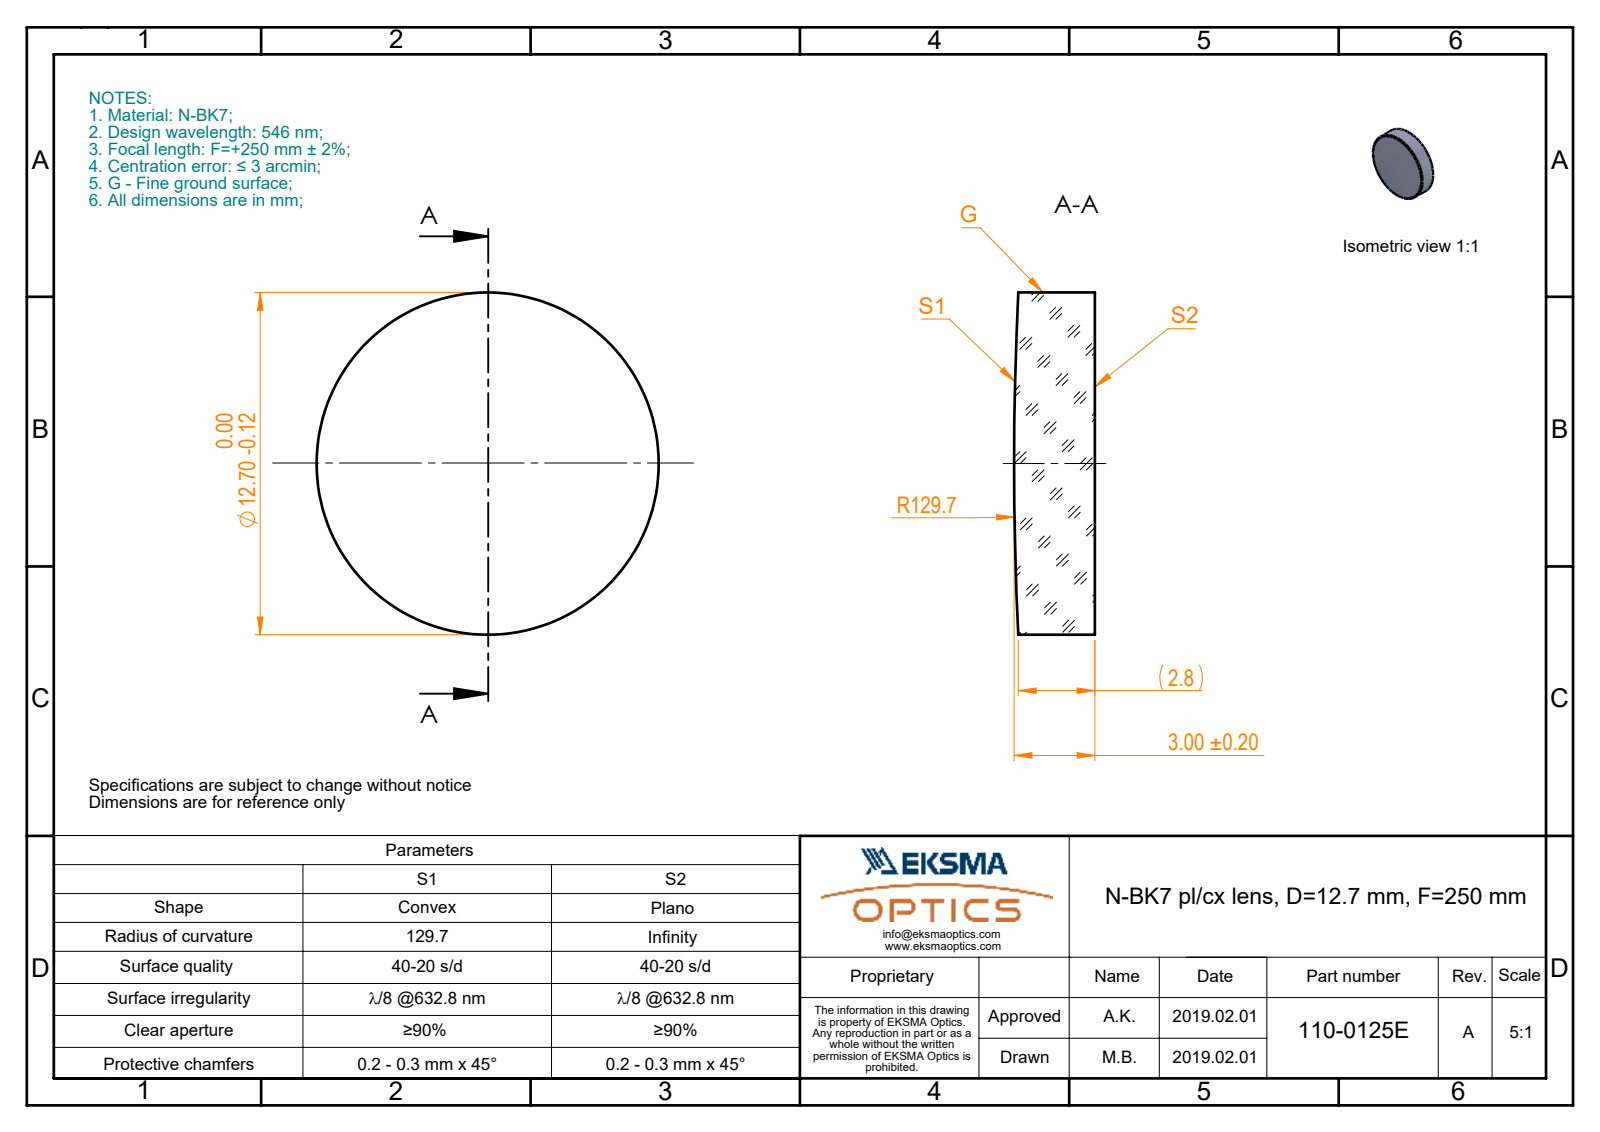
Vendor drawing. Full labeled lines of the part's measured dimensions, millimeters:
Part name (STEP PRODUCT): 110-0125E BK7 pl-cx 12.7 F250
STEP written by: SolidWorks 2017 (CONFIG_CONTROL_DESIGN)
Units: millimetres
Bodies: 1 solid, 5 faces (1 planar, 2 cylindrical, 2 other)
Overall size (bounding box): 12.7 × 12.7 × 3
Volume: 370 mm³ · Surface area: 367 mm²
Round bosses / shafts (diameter × count): ⌀12.7 ×1
